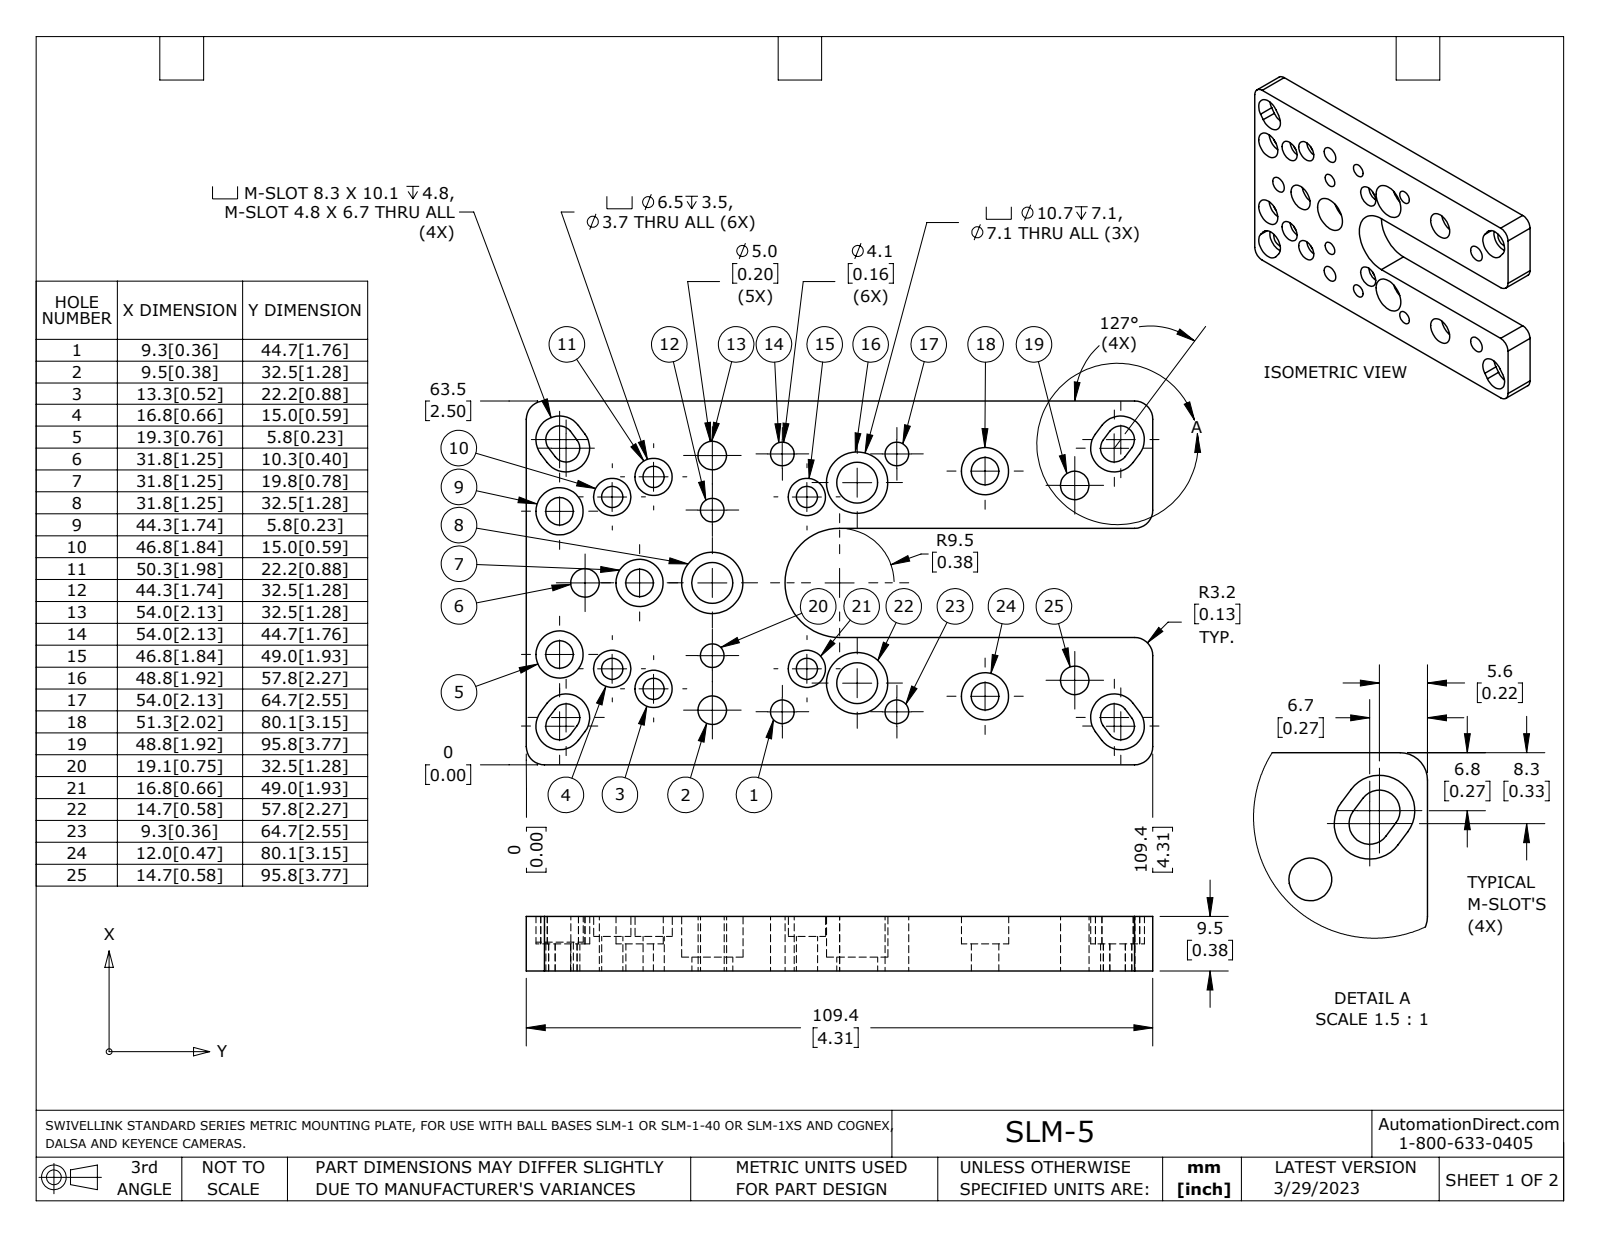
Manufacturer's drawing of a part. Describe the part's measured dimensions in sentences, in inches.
The part is named "SLM-5". Its 3-D file was written by "SolidWorks 2021 (AUTOMOTIVE_DESIGN)". It is 1 solid with 105 faces: 43 planar, 62 cylindrical and 0 other. Overall it measures 4.307 by 2.5 by 0.375 inches. Its volume is 2.822 cubic inches and its surface area 30.77 square inches. Round holes: 6 of diameter 0.146, 6 of diameter 0.163, 6 of diameter 0.256, 5 of diameter 0.189, 5 of diameter 0.196, 5 of diameter 0.325, 3 of diameter 0.281, 3 of diameter 0.422. Partial cylindrical surfaces (rounded edges, fillets, slot ends): 8 of radius 0.094, 8 of radius 0.162, 6 of radius 0.125, 1 of radius 0.375. The main face-to-face distances are 0.375, 0.875, 1.625, 2.5, 0.75, 4.307, 0.189, 0.186, 0.28, 0.091. The hole center spacings are 0.375, 1.007, 1.979, 0.5, 0.875, 1.547, 0.316, 0.336.
